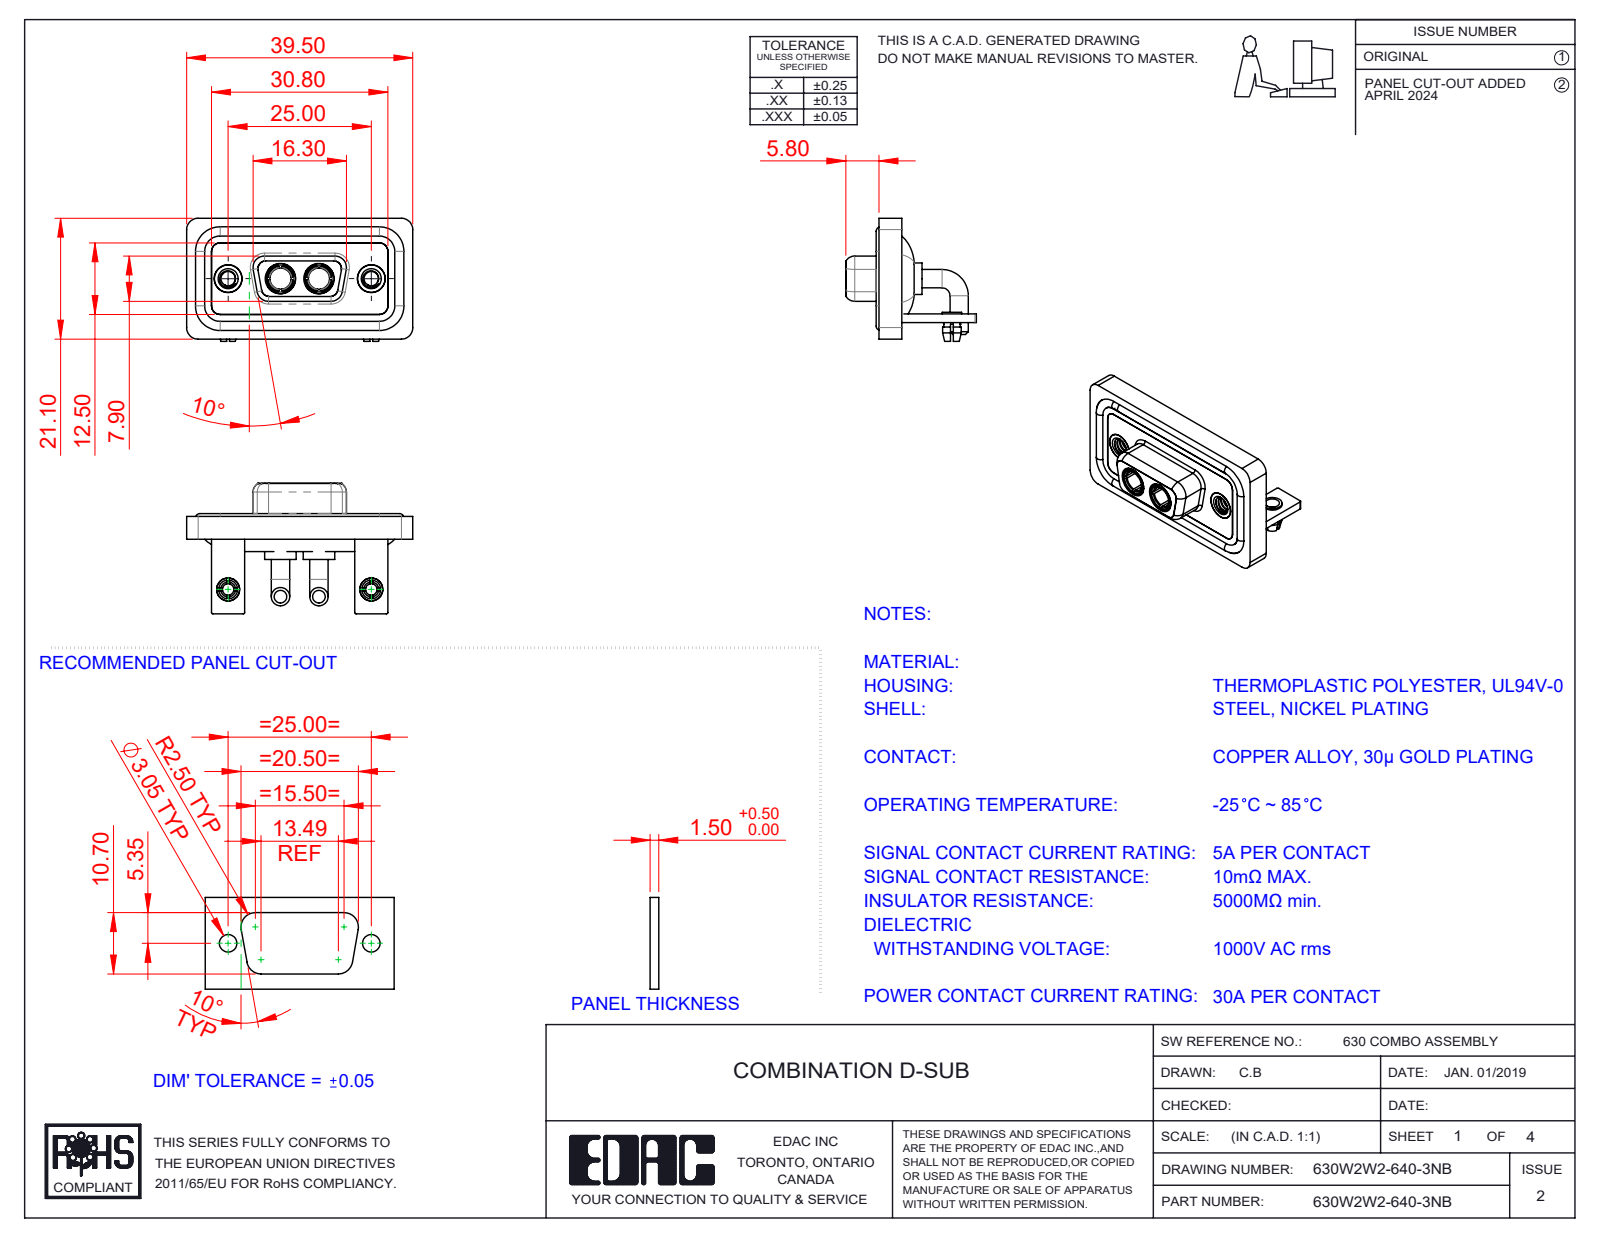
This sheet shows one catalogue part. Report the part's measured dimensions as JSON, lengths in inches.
{"part_name": "630Combo Board Lock_50 Contacts; 630Combo Stabilizer Bracket_50 Contacts; 630Combo Shell Rear_09 Contacts; 630Combo Threaded Rivet_A (+5 more)", "step_written_by": "SolidWorks 2023 (CONFIG_CONTROL_DESIGN)", "units": "inches", "bodies": {"solids": 15, "faces": 676, "planar": 231, "cylindrical": 292, "other": 153}, "overall_size": [1.555, 0.898, 0.846], "volume_in3": 0.321, "surface_area_in2": 13.6, "round_holes": [[0.098, 4], [0.191, 4], [0.079, 2], [0.126, 2], [0.146, 2], [0.157, 2], [0.159, 2], [0.197, 2], [0.209, 2]], "round_bosses_or_shafts": [[0.126, 4], [0.063, 4], [0.217, 2], [0.205, 2], [0.195, 2], [0.195, 2], [0.189, 2], [0.187, 2]], "partial_cylinders_radius": [[0.079, 19], [0.059, 18], [0.01, 16], [0.053, 8], [0.063, 8], [0.02, 5], [0.024, 4], [0.026, 4]], "face_to_face_distances": [0.016, 0.114, 0.059, 0.071, 0.043, 0.146, 0.031, 0.098, 0.063, 0.122], "hole_center_spacings": [0.36, 0.624, 0.984, 0.265]}
